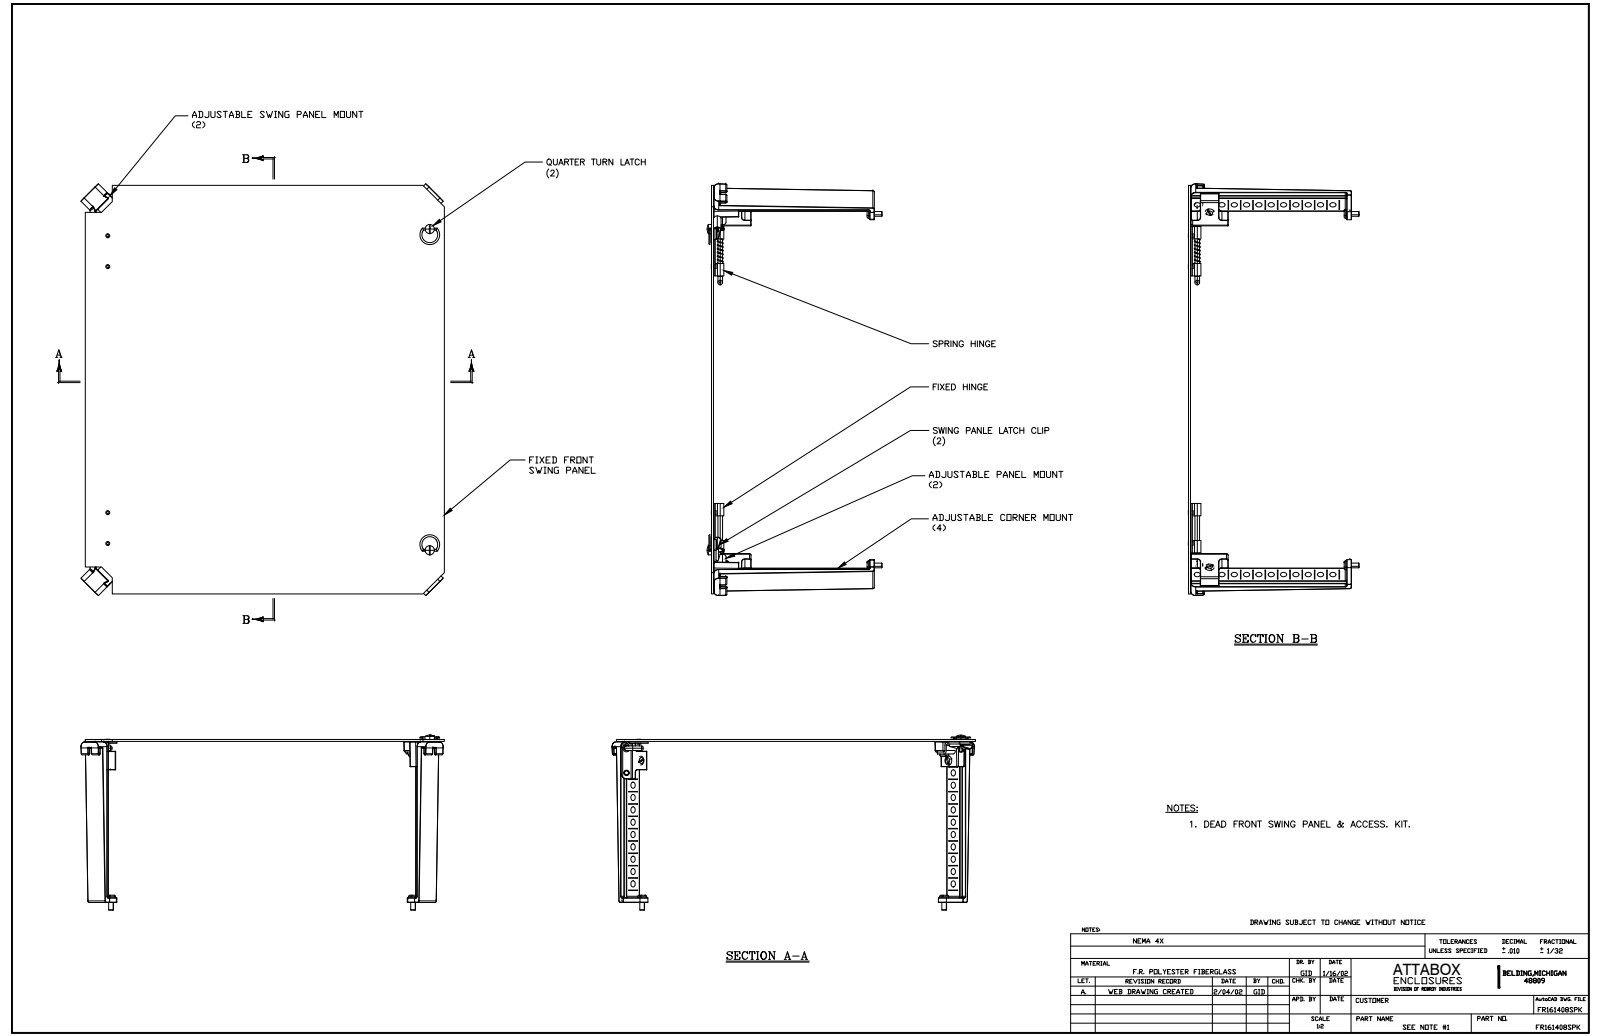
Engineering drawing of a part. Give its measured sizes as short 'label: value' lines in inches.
name: FR161408SPK
written by: SolidWorks 2019 (AUTOMOTIVE_DESIGN)
unit: in
bodies: 48 solids, 2225 faces (1070 planar, 493 cylindrical, 662 other)
size: 16.688 × 14.749 × 7.184
volume: 30.8 in³; area: 642.9 in²
holes: 52× ⌀0.25, 6× ⌀0.156, 6× ⌀0.253, 4× ⌀0.05, 4× ⌀0.14, 4× ⌀0.144, 4× ⌀0.217, 4× ⌀0.22, 3× ⌀0.312, 2× ⌀0.153, 2× ⌀0.197, 2× ⌀0.35
bosses: 10× ⌀0.19, 6× ⌀0.373, 6× ⌀0.246, 5× ⌀0.16, 4× ⌀0.433, 4× ⌀0.315, 4× ⌀0.079, 3× ⌀0.187
rounds: 214× R0.01, 44× R0.06, 16× R0.063, 8× R0.025, 8× R0.13, 4× R0.049, 4× R0.125, 4× R0.19
face distances: 0.08, 19.78, 8.683, 11.097, 9.682, 10.097, 1, 1.415, 0.203, 8.886
hole spacings: 0.5, 1.5, 1, 1.5, 1.733, 2.062, 2, 2.45
